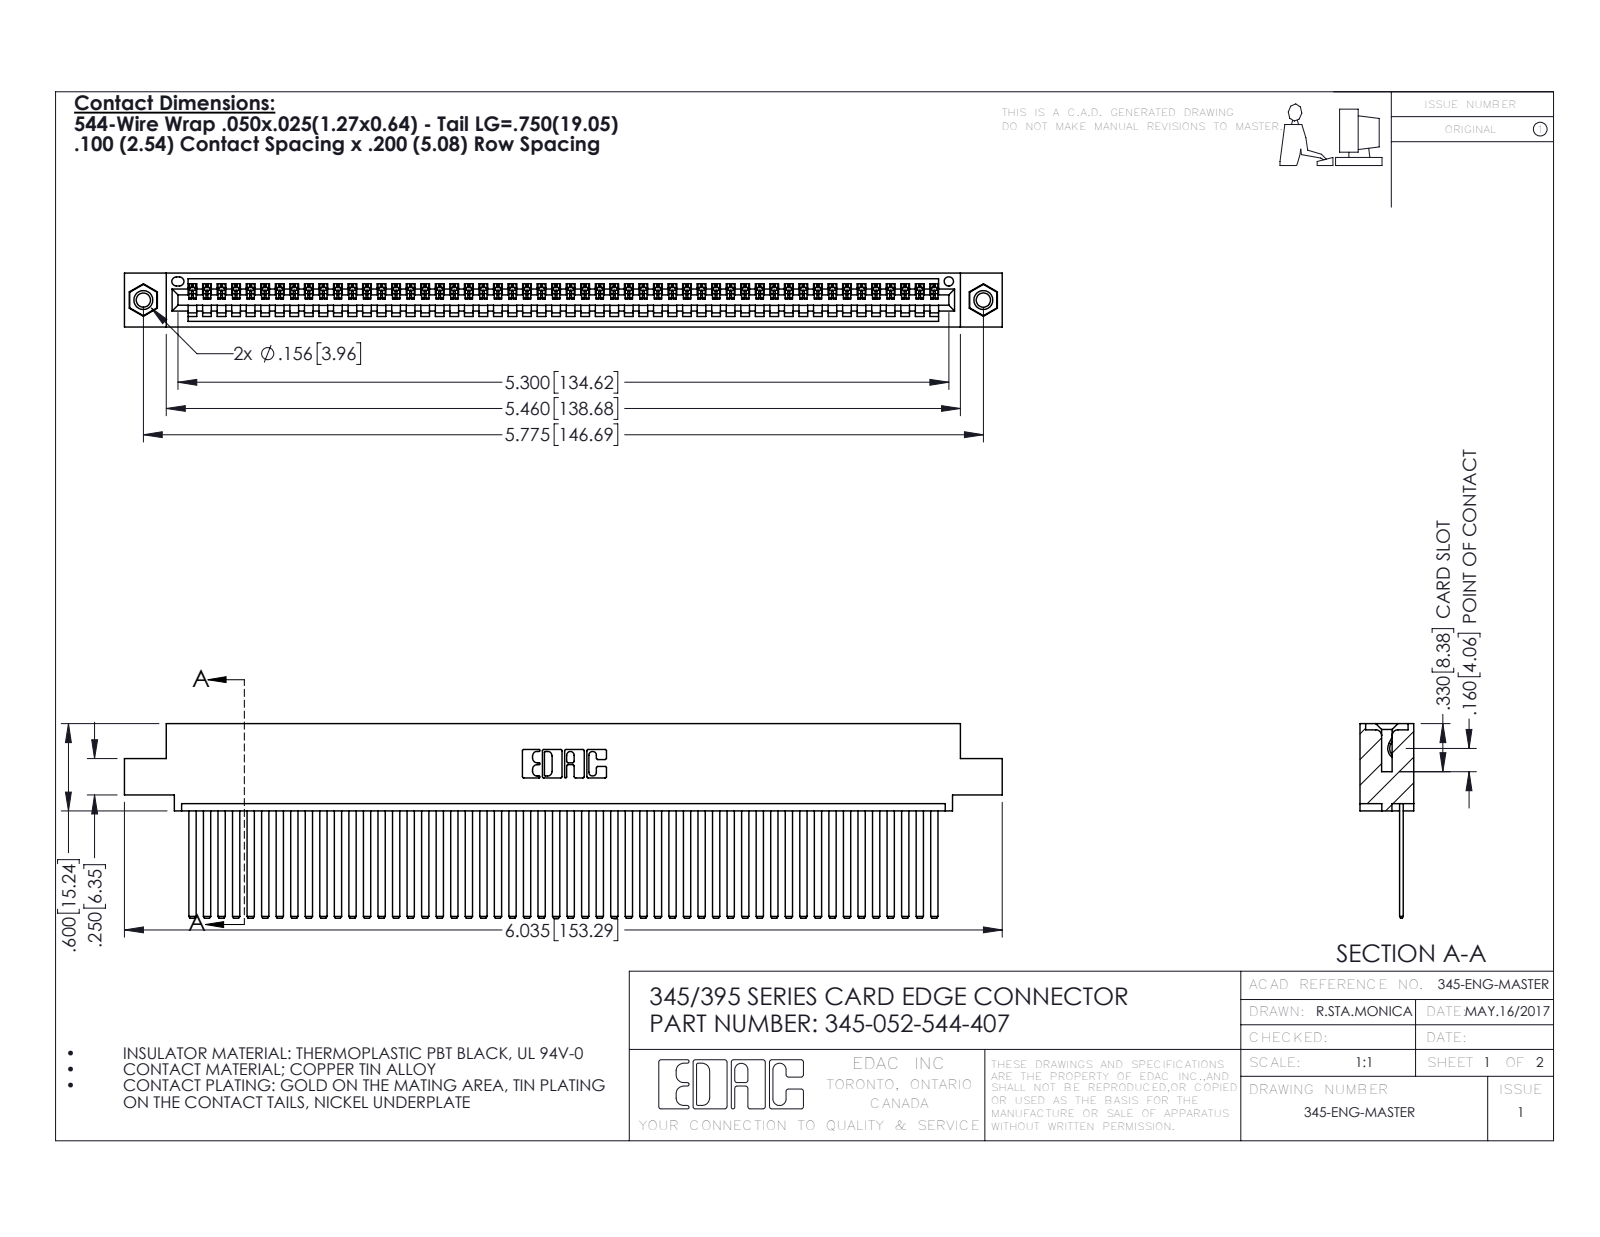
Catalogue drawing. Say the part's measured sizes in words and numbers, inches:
The part is named "345-292-001_345-293-144; 345-052-544-407; 345-250-001_345-250-005-103; 345 Part_0.110 Offset - 0.156 Dia-TI". Its 3-D file was written by "SolidWorks 2016 (CONFIG_CONTROL_DESIGN)". It is 55 solids with 2894 faces: 1988 planar, 890 cylindrical and 16 other. Overall it measures 6.035 by 1.337 by 0.37 inches. Its volume is 0.925 cubic inches and its surface area 34.41 square inches. Round holes: 2 of diameter 0.098, 2 of diameter 0.125, 2 of diameter 0.156, 1 of diameter 0.064. Round bosses or shafts: 2 of diameter 0.155. Partial cylindrical surfaces (rounded edges, fillets, slot ends): 104 of radius 0.006, 22 of radius 0.01, 6 of radius 0.007, 6 of radius 0.031, 3 of radius 0.026, 2 of radius 0.031, 2 of radius 0.04, 1 of radius 0.014. The main face-to-face distances are 0.072, 0.298, 0.025, 0.098, 0.272, 0.37, 0.2, 0.225, 0.149, 0.072. The hole center spacings are 0.27, 5.539, 5.775.
